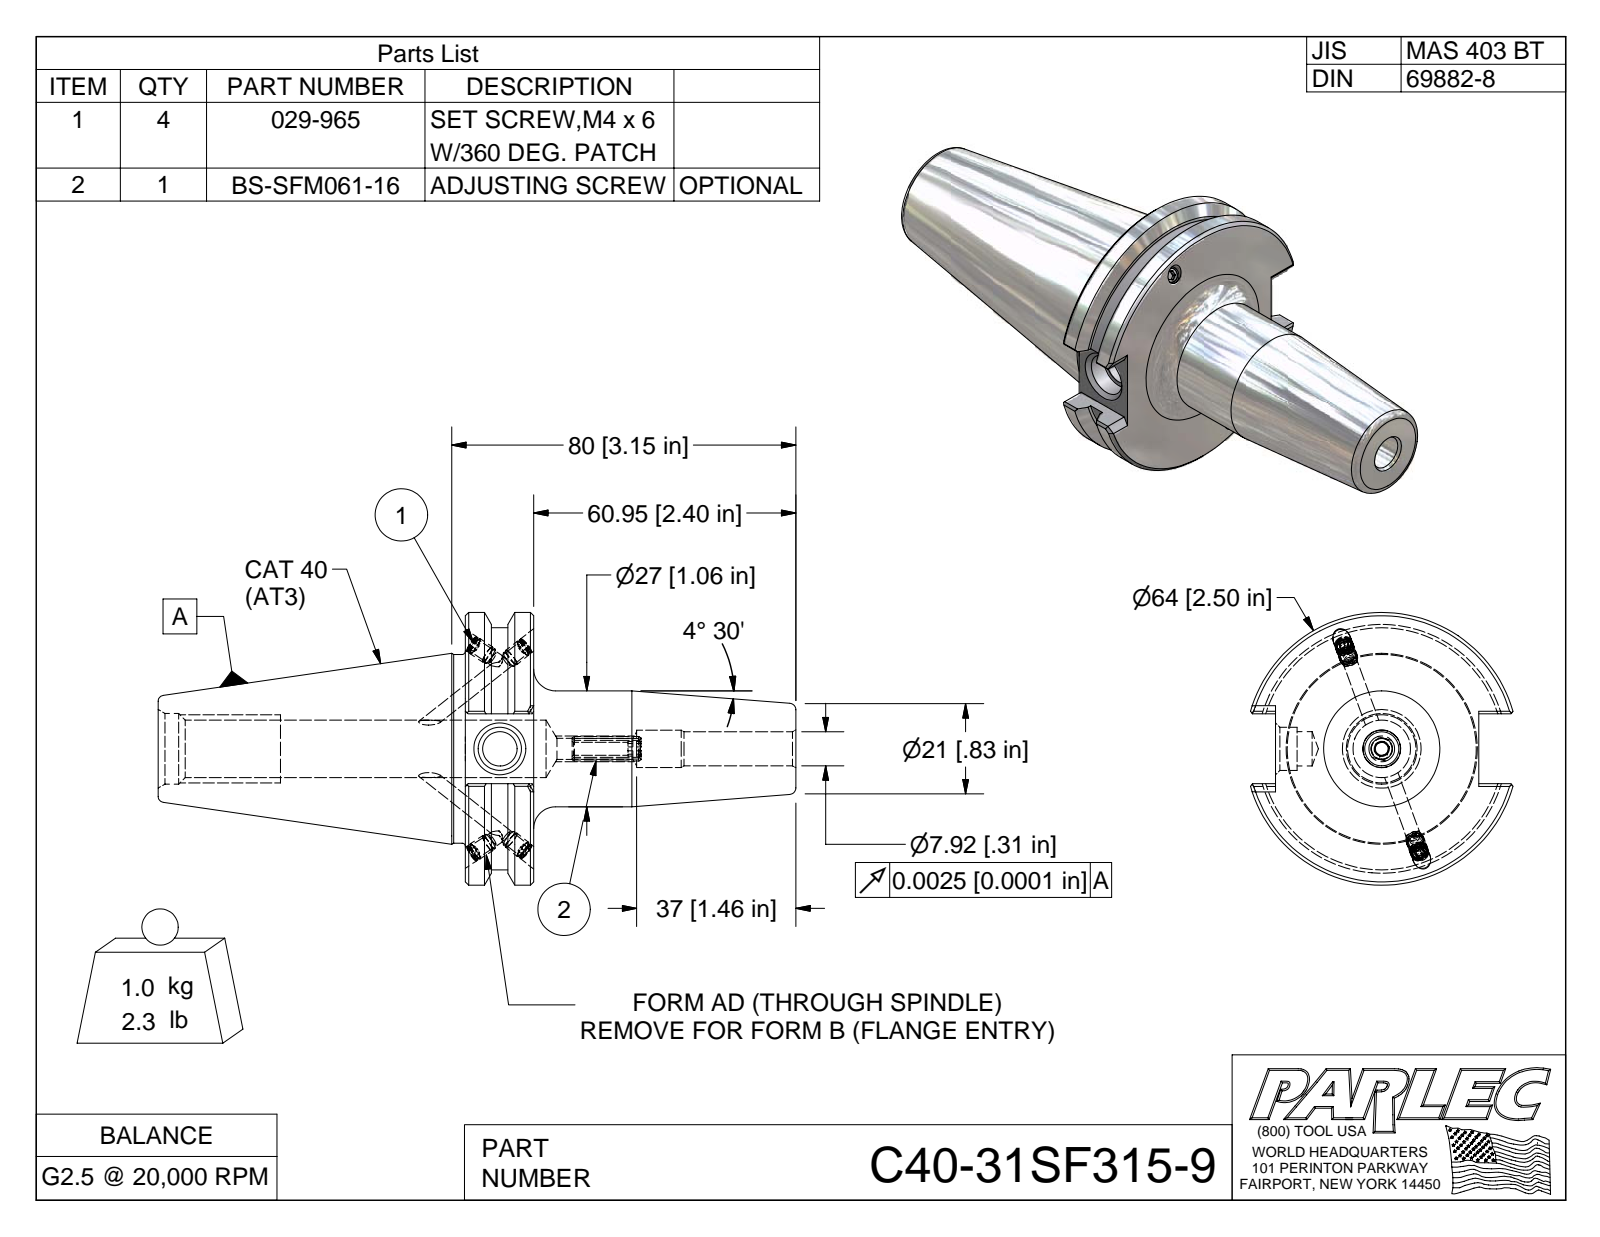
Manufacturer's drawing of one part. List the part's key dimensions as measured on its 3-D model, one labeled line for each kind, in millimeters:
Part name (STEP PRODUCT): C40-31SF315-9; C40BC-31SF315-9-1; 029-965; BS-SFM061-16
STEP written by: Autodesk Inventor 2009 (AUTOMOTIVE_DESIGN)
Units: millimetres
Bodies: 6 solids, 177 faces (87 planar, 32 cylindrical, 58 other)
Overall size (bounding box): 148.3 × 63.5 × 61
Volume: 128 200 mm³ · Surface area: 27 880 mm²
Round holes (diameter × count): ⌀3.3 ×4, ⌀4.1 ×4, ⌀7.9 ×1, ⌀8.7 ×1
Round bosses / shafts (diameter × count): ⌀4.2 ×4, ⌀4 ×4, ⌀63.5 ×1, ⌀56.4 ×1, ⌀43.9 ×1, ⌀27 ×1
Partial cylindrical surfaces — rounded edges, fillets, slot ends (radius × count): R3 ×1
Main face-to-face distances: 15.9, 76.8, 61, 16.3, 47.2, 71.4, 87.3, 148.3, 81.3, 9.9
